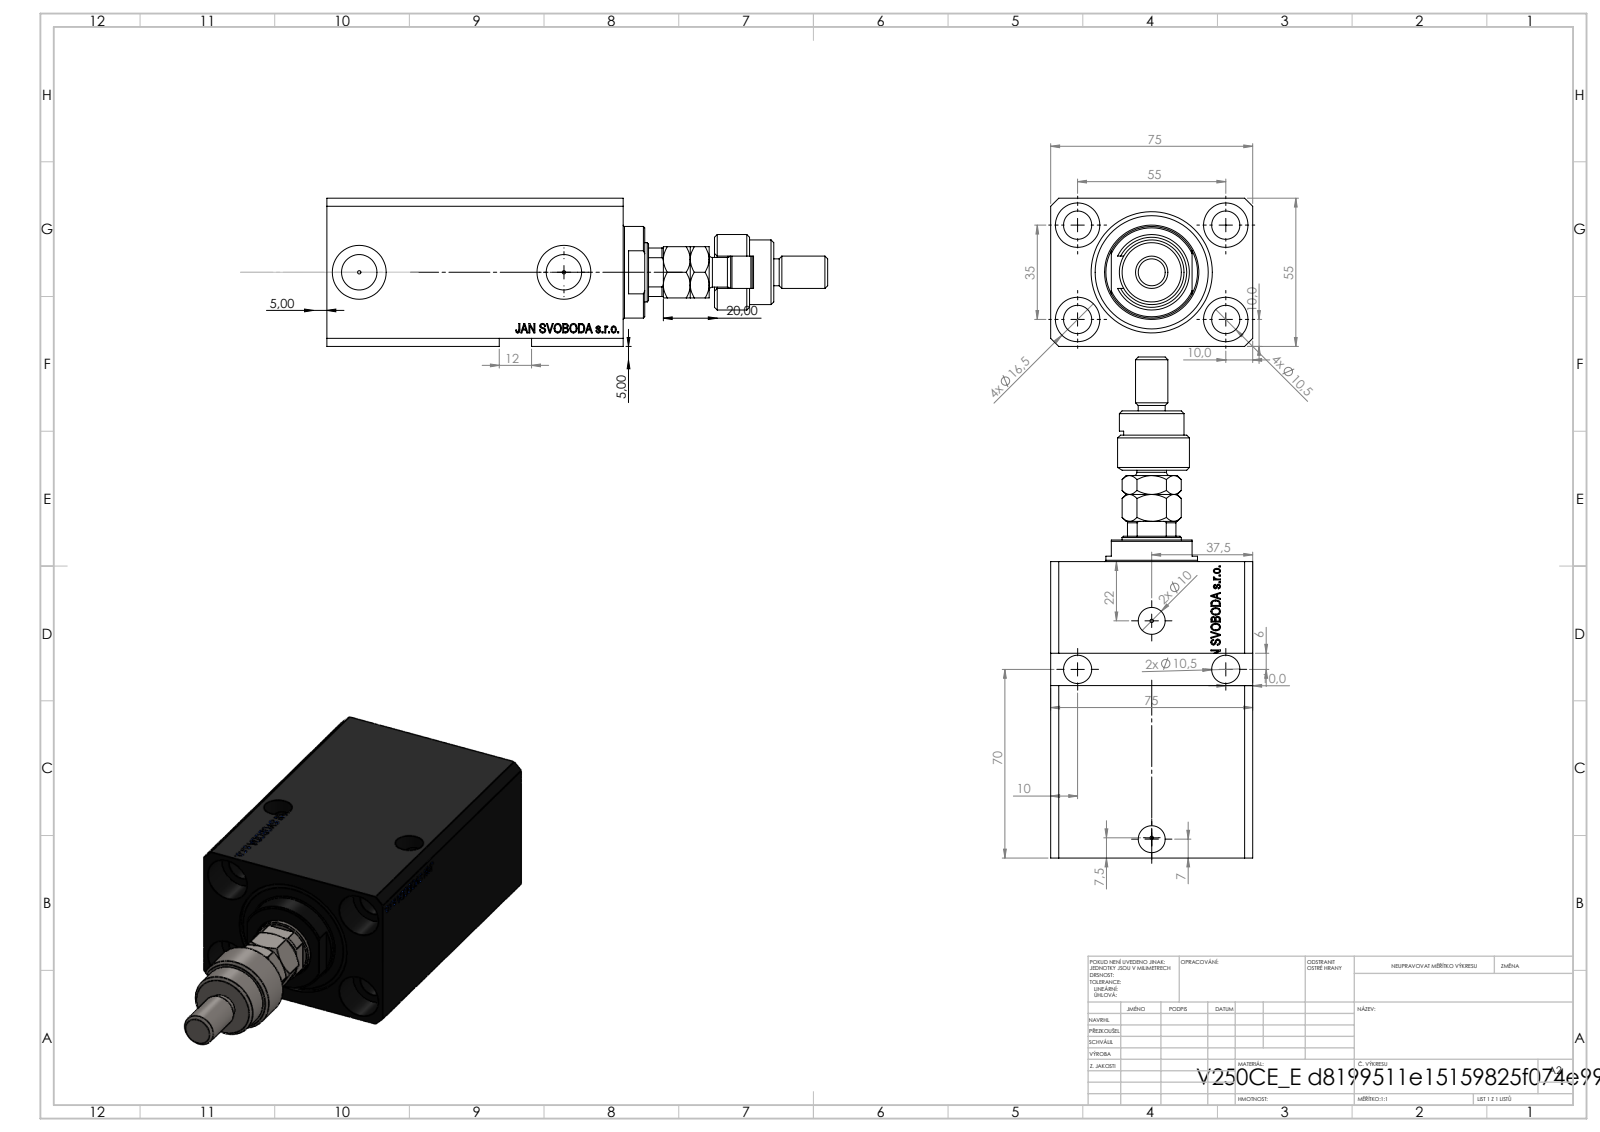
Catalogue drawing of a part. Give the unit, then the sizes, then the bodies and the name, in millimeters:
Units: millimetres
Overall size (bounding box): 186 × 75 × 55
Round holes (diameter × count): ⌀10.5 ×9, ⌀1.25 ×4, ⌀16.5 ×4, ⌀10 ×2, ⌀13.16 ×2, ⌀20 ×2, ⌀22 ×1, ⌀32 ×1, ⌀45 ×1
Round bosses / shafts (diameter × count): ⌀34 ×1, ⌀28 ×1, ⌀24 ×1, ⌀18 ×1, ⌀12 ×1, ⌀11 ×1, ⌀10 ×1
Partial cylindrical surfaces — rounded edges, fillets, slot ends (radius × count): R9.75 ×1, R10.5 ×1
Main face-to-face distances: 55, 75, 15, 110, 95, 19, 9.9, 85.1, 100.1, 99
Hole centre spacings: 32.6, 32.87, 55, 68.74, 32.58, 35, 45, 65.19
Volume: 386 993 mm³ · Surface area: 92 511 mm²
Bodies: 5 solids, 999 faces (466 planar, 117 cylindrical, 416 other)
Part name (STEP PRODUCT): FEMALE_PART_FOR_DFA; V250CE_E_Body; MFA; V250CE_VC_E (+1 more)
STEP written by: SolidWorks 2019 (CONFIG_CONTROL_DESIGN)
